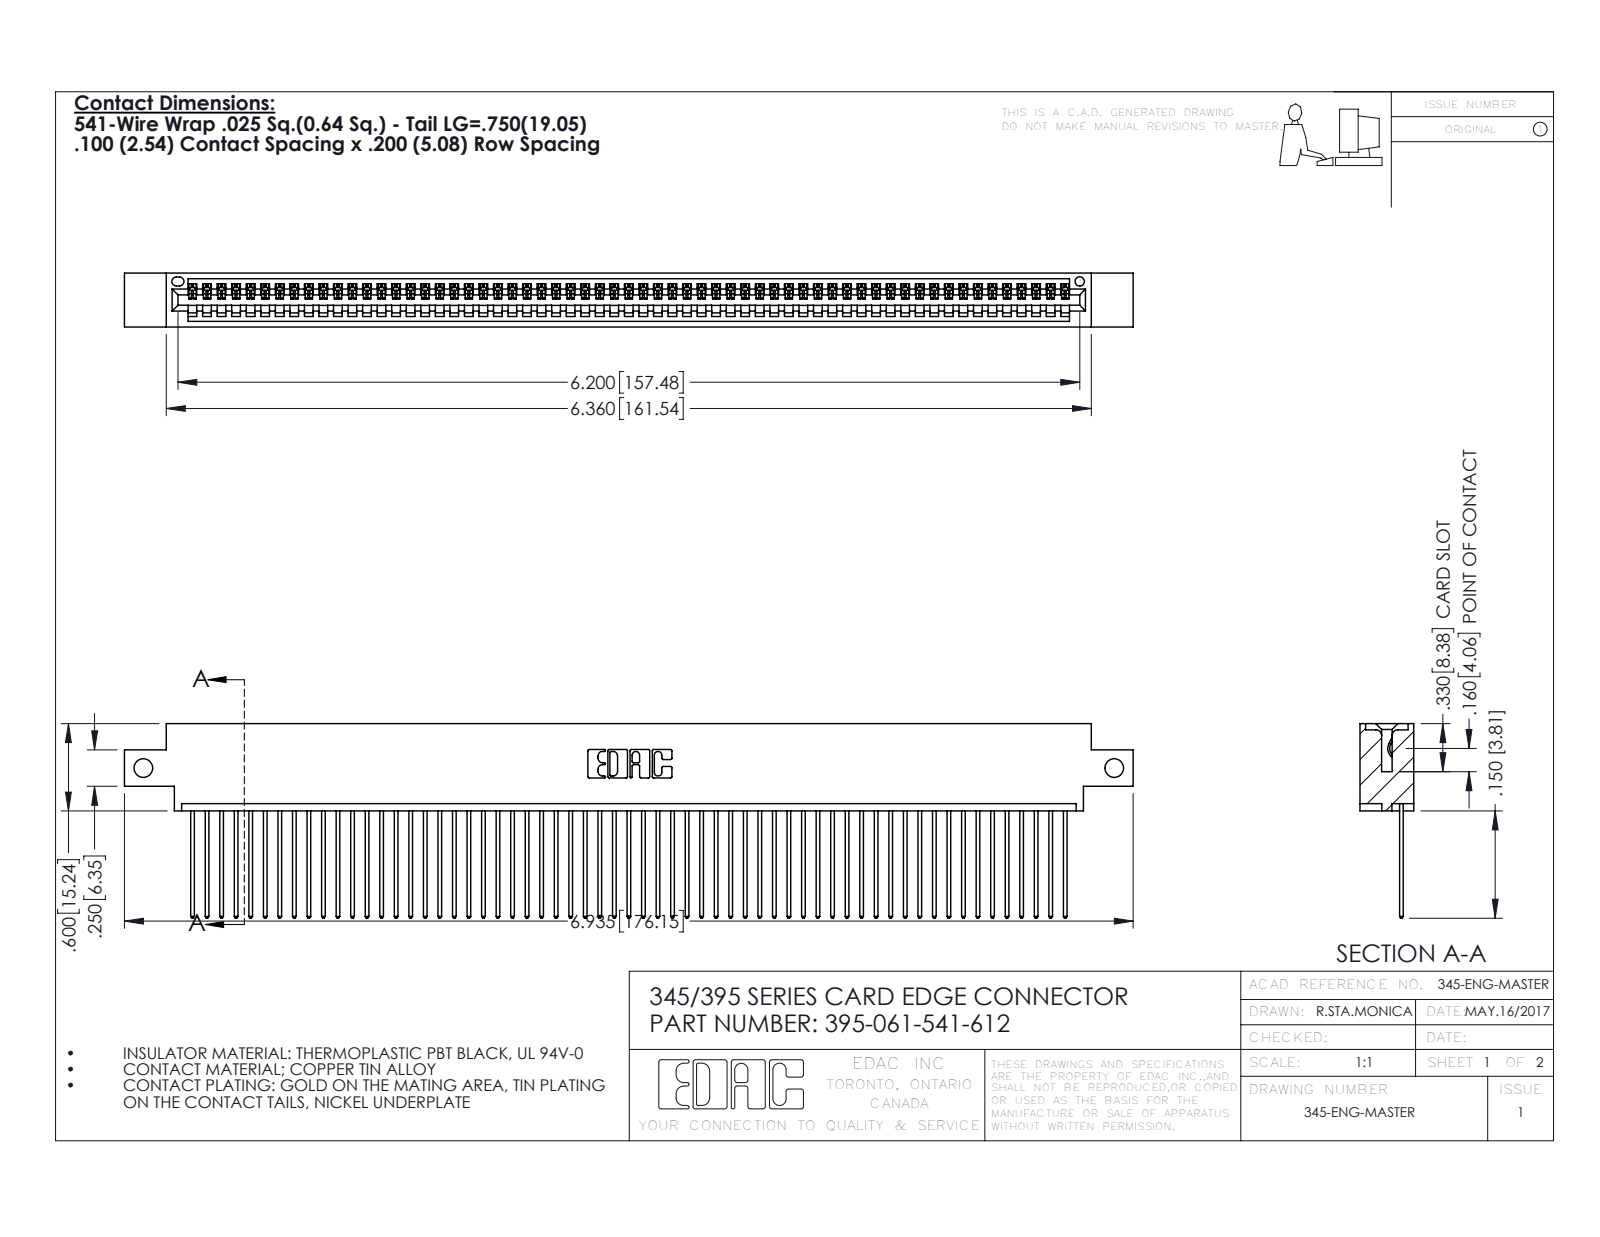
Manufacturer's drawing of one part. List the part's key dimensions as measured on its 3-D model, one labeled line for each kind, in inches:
Part name (STEP PRODUCT): 345-292-001_345-293-141; 395-061-541-612; 345 Part_0.170 Offset - Side Mount
STEP written by: SolidWorks 2016 (CONFIG_CONTROL_DESIGN)
Units: inches
Bodies: 62 solids, 3668 faces (2524 planar, 1144 cylindrical, 0 other)
Overall size (bounding box): 6.935 × 1.337 × 0.37
Volume: 1.031 in³ · Surface area: 37 in²
Round holes (diameter × count): ⌀0.128 ×2, ⌀0.064 ×1
Partial cylindrical surfaces — rounded edges, fillets, slot ends (radius × count): R0.006 ×122, R0.01 ×122, R0.01 ×22, R0.007 ×6, R0.031 ×6, R0.026 ×3, R0.031 ×2, R0.04 ×2
Main face-to-face distances: 0.072, 0.298, 0.098, 0.272, 0.025, 0.37, 0.2, 0.225, 0.175, 0.149
Hole centre spacings: 6.675
